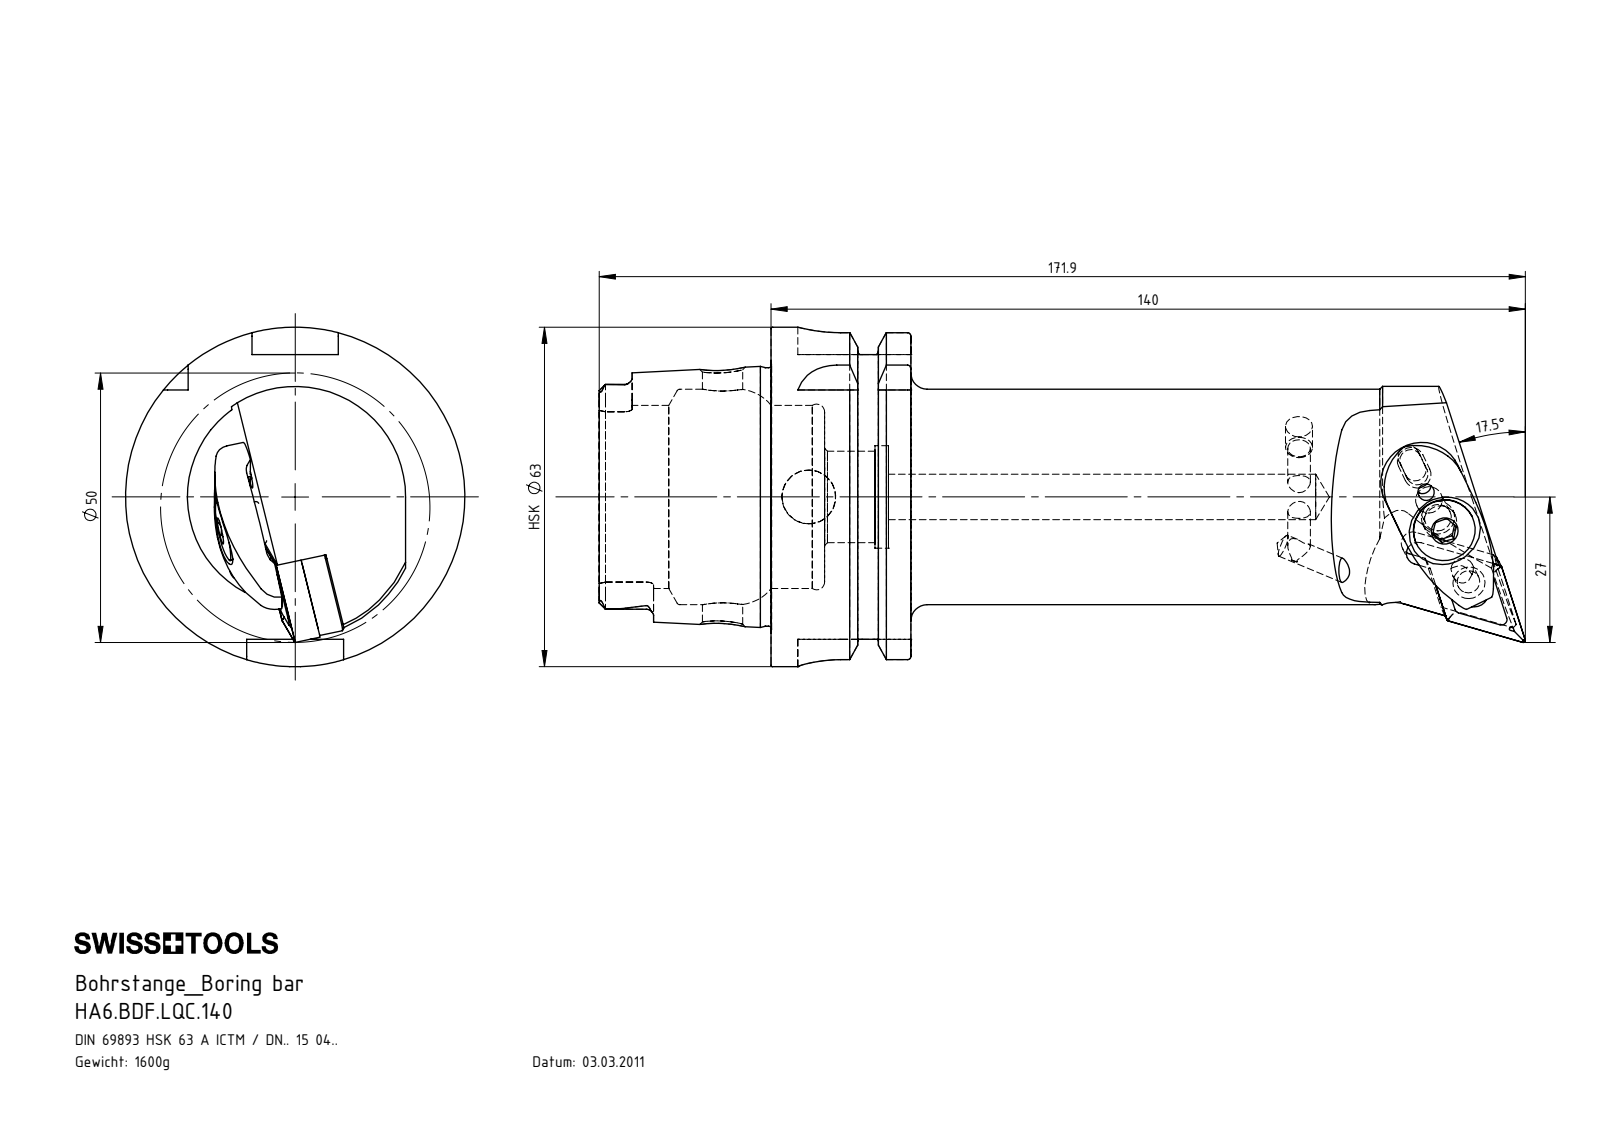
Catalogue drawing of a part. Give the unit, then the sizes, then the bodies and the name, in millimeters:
Units: millimetres
Overall size (bounding box): 171.9 × 63 × 63
Round holes (diameter × count): ⌀4.2 ×3, ⌀5 ×2, ⌀3 ×1, ⌀4 ×1, ⌀5.16 ×1, ⌀6.2 ×1, ⌀6.5 ×1, ⌀7 ×1, ⌀7.5 ×1, ⌀8.4 ×1, ⌀10 ×1, ⌀17 ×1
Round bosses / shafts (diameter × count): ⌀5 ×2, ⌀63 ×1, ⌀54.95 ×1, ⌀47.94 ×1, ⌀11.5 ×1, ⌀7 ×1, ⌀6.2 ×1, ⌀6 ×1
Partial cylindrical surfaces — rounded edges, fillets, slot ends (radius × count): R0.39 ×6, R0.69 ×6, R1.4 ×6, R0.4 ×5, R8 ×4, R3 ×3, R2 ×2, R2.82 ×2
Main face-to-face distances: 25.95, 16, 9.95, 31.9, 41.85, 57.85, 6.05, 52.8, 21.8, 3.18
Hole centre spacings: 14.81, 23, 8, 8.19, 15, 15.01
Volume: 204 967 mm³ · Surface area: 42 425 mm²
Bodies: 9 solids, 411 faces (111 planar, 132 cylindrical, 168 other)
Part name (STEP PRODUCT): WCC-ER3.102.024_C; KVT_MB_600_050; DNMG150604; WDF-ER2.101.003_A (+5 more)
STEP written by: SolidWorks 2022 (CONFIG_CONTROL_DESIGN)
